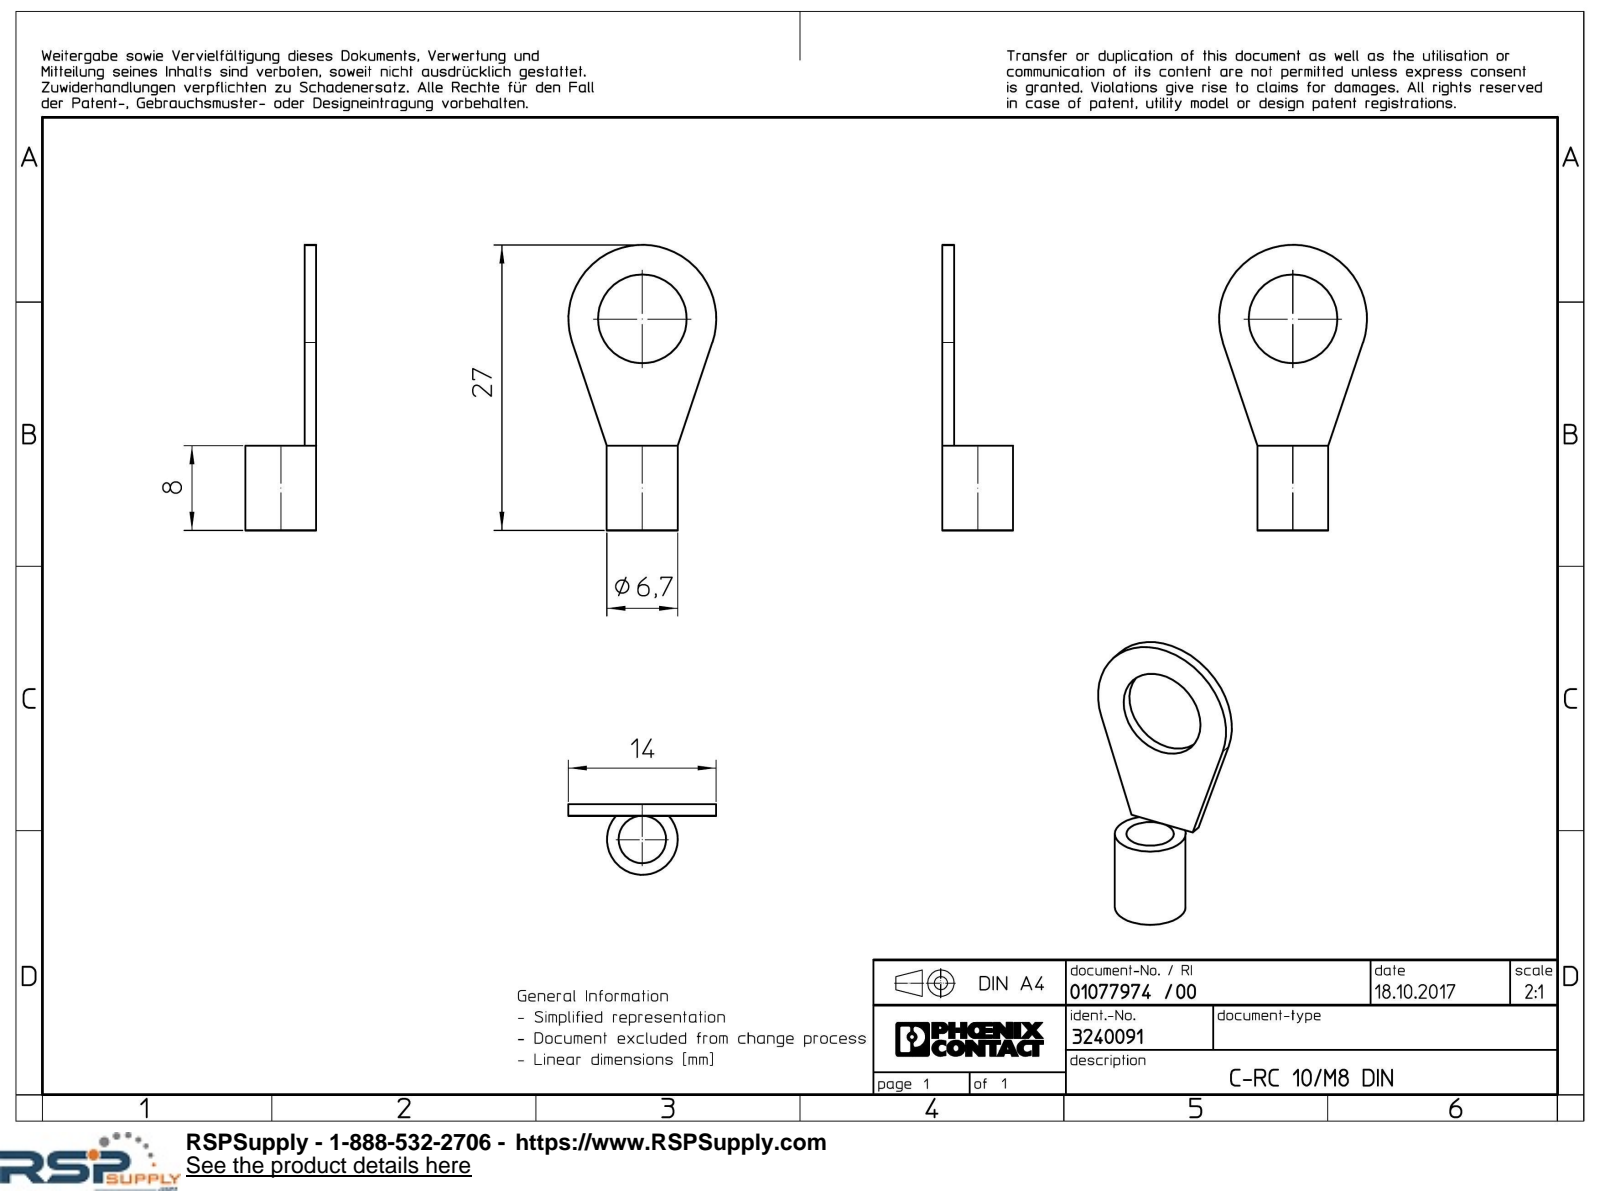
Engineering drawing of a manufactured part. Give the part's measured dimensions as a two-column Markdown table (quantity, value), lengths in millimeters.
| quantity | value |
| --- | --- |
| part name | C_RC_10_M8_DIN-select |
| STEP written by | Creo Elements/Direct Modeling 18.1I 14-Aug-2016 (C) Parametric Technology GmbH (AUTOMOTIVE_DESIGN) |
| units | millimeters |
| bodies | 1 solid, 15 faces (8 planar, 7 cylindrical, 0 other) |
| overall size | 27 × 14 × 6.7 |
| volume | 320 mm³ |
| surface area | 700 mm² |
| round holes (diameter × count) | 4.5 × 1, 8.4 × 1 |
| round bosses / shafts (diameter × count) | 6.7 × 1 |
| partial cylindrical surfaces (radius × count) | 7 × 1 |
| main face-to-face distances | 1.1, 8 |
